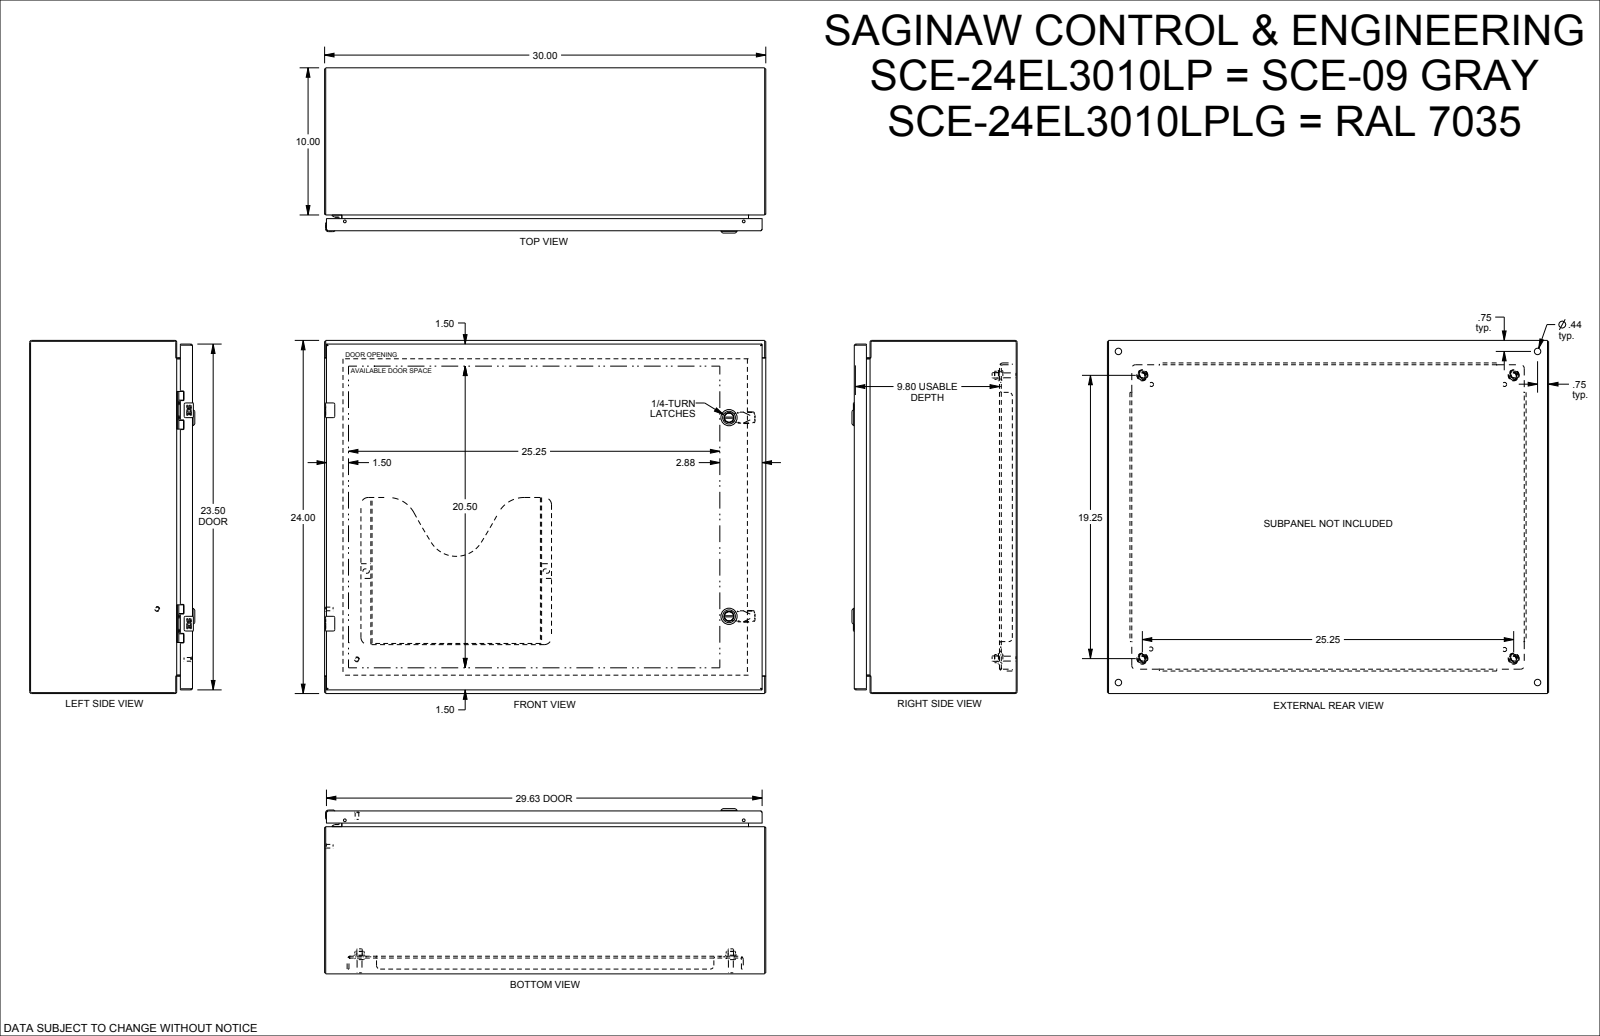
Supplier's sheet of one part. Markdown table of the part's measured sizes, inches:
| quantity | value |
| --- | --- |
| part name | SCE-24EL3010LP |
| STEP written by | SolidWorks 2021 (AUTOMOTIVE_DESIGN) |
| units | inches |
| bodies | 47 solids, 2843 faces (1115 planar, 858 cylindrical, 870 other) |
| overall size | 30 × 24 × 11.23 |
| volume | 303.2 in³ |
| surface area | 7 319 in² |
| round holes (diameter × count) | 0.172 × 4, 0.205 × 4, 0.244 × 4, 0.266 × 4, 0.281 × 4, 0.367 × 4, 0.375 × 4, 0.437 × 4, 0.5 × 4, 0.04 × 2, 0.188 × 2, 0.197 × 2 |
| round bosses / shafts (diameter × count) | 0.17 × 6, 0.366 × 4, 0.332 × 4, 0.25 × 4, 0.248 × 4, 0.24 × 4, 0.196 × 3, 1.102 × 2 |
| partial cylindrical surfaces (radius × count) | 0.012 × 56, 0.01 × 28, 0.015 × 24, 0.02 × 20, 0.04 × 17, 0.06 × 13, 0.029 × 12, 0.1 × 12 |
| main face-to-face distances | 0.075, 0.06, 10.998, 11.073, 11.013, 10.938, 0.075, 1.2, 9.873, 1.125 |
| hole center spacings | 14.5, 0.02, 0.493, 0.985, 0.875, 3.173, 4.493, 20.38 |
